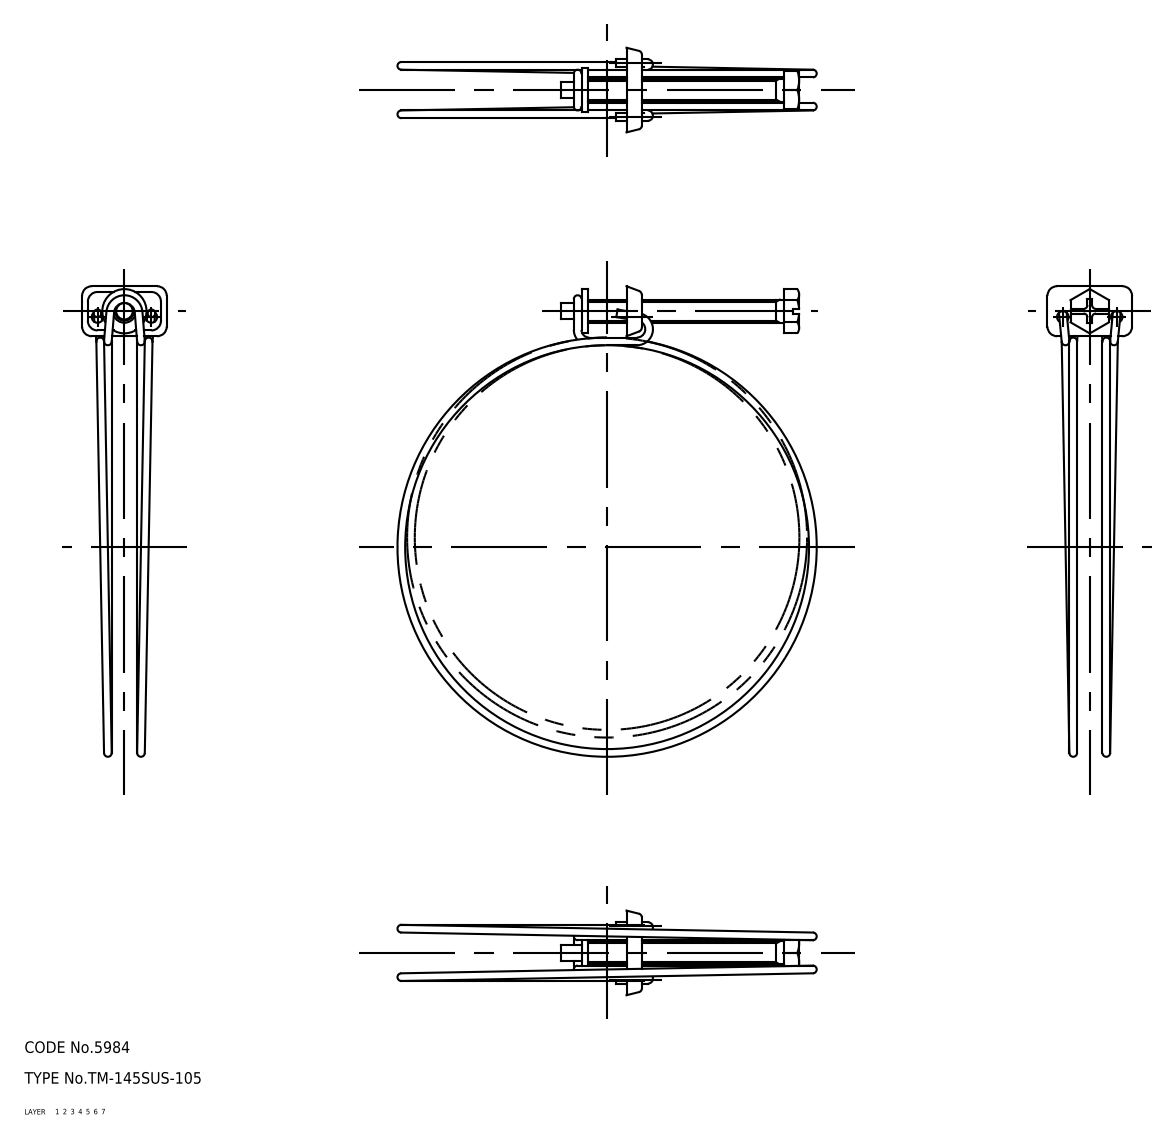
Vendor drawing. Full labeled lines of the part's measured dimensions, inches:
Part name (STEP PRODUCT): screw; holder; band; TM_145SUS_105_21011_36
STEP written by: CADfix (AUTOMOTIVE_DESIGN)
Units: inches
Bodies: 3 solids, 119 faces (0 planar, 0 cylindrical, 119 other)
Overall size (bounding box): 4.817 × 4.291 × 0.866
Volume: 0.298 in³ · Surface area: 11.1 in²
